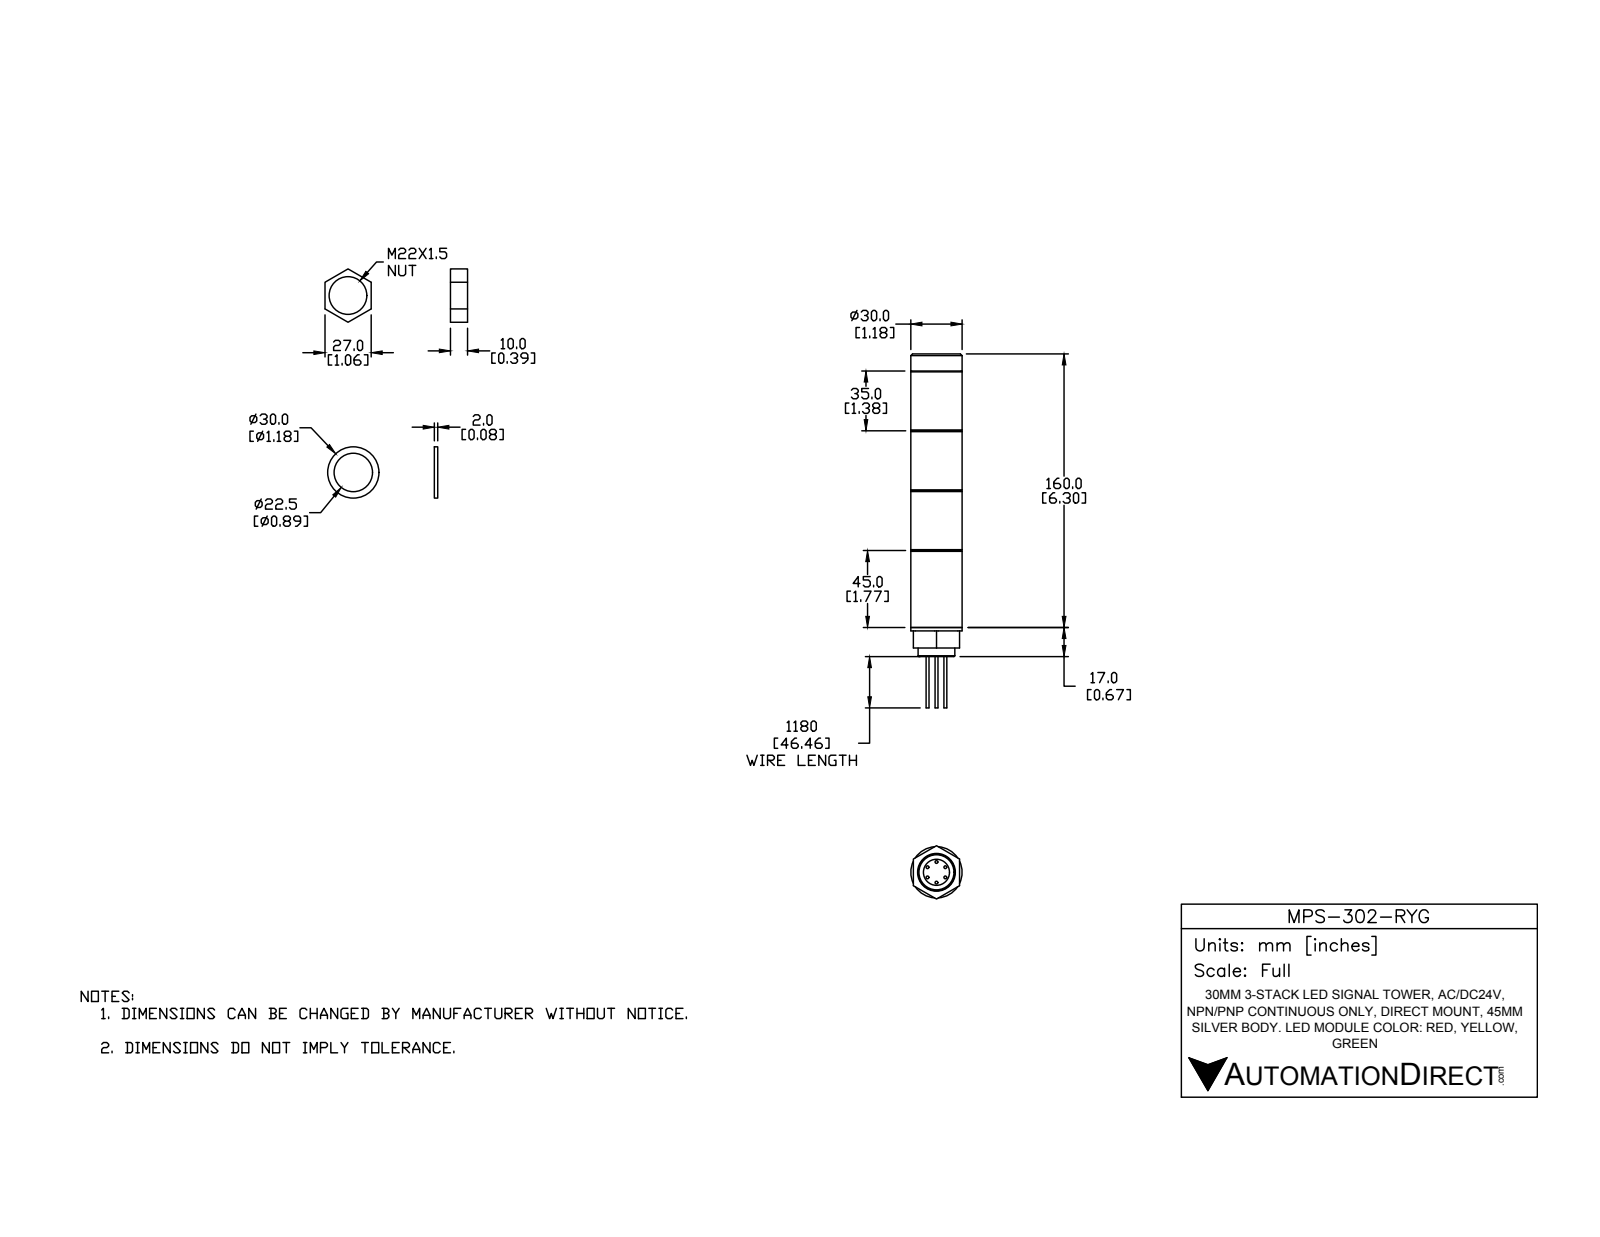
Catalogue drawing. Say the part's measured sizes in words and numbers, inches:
The part is named "MPS-302-RYG". Its 3-D file was written by "SolidWorks 2016 (AUTOMOTIVE_DESIGN)". It is 14 solids with 111 faces: 51 planar, 40 cylindrical and 20 other. Overall it measures 8.15 by 1.228 by 1.181 inches. Its volume is 6.654 cubic inches and its surface area 49.97 square inches. Round holes: 1 of diameter 0.126, 1 of diameter 0.303, 1 of diameter 0.602, 1 of diameter 0.815, 1 of diameter 0.866. Round bosses or shafts: 6 of diameter 0.067, 1 of diameter 1.181, 1 of diameter 0.846, 1 of diameter 0.197. The main face-to-face distances are 1.378, 2.756, 1.772, 3.15, 4.528, 4.134, 1.85, 3.228, 4.606, 6.378.
